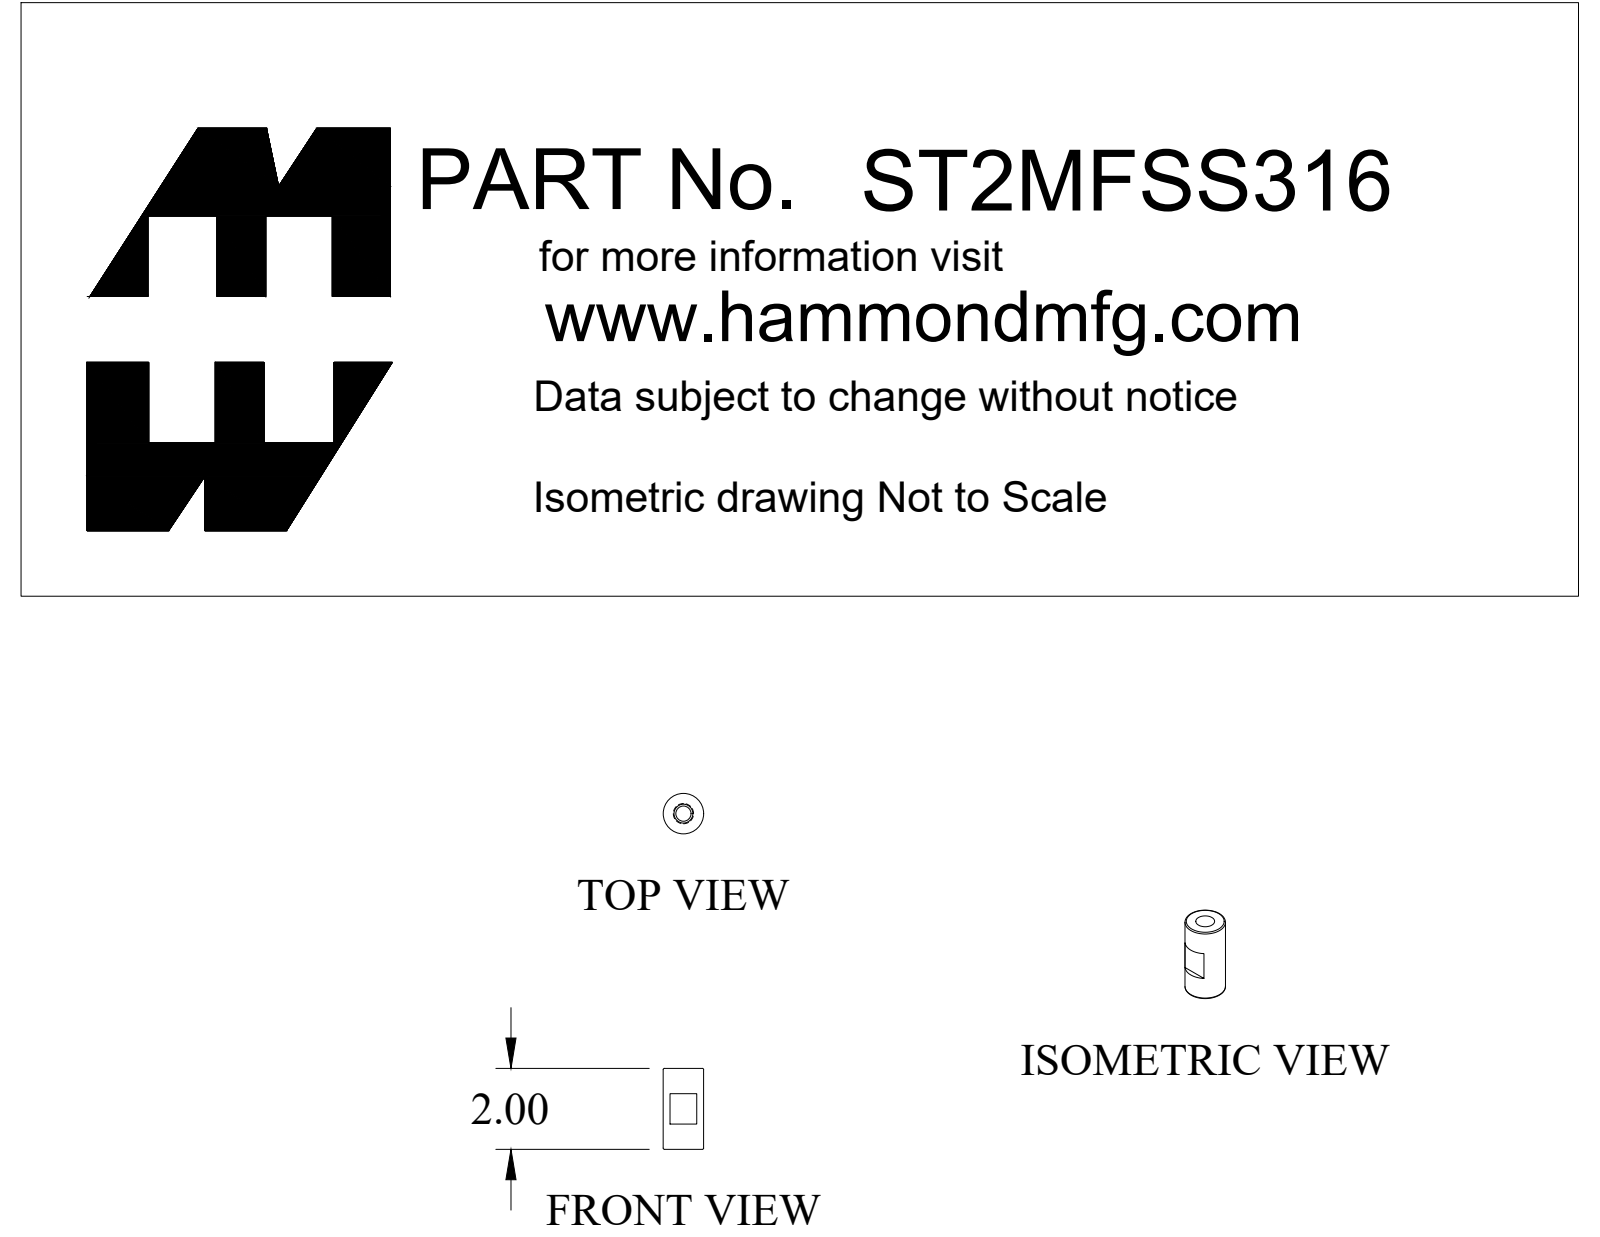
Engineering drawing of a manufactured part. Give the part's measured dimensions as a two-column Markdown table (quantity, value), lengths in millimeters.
| quantity | value |
| --- | --- |
| part name | ST2MFSS316 |
| STEP written by | SolidWorks 2019 (CONFIG_CONTROL_DESIGN) |
| units | millimeters |
| bodies | 3 solids, 31 faces (21 planar, 7 cylindrical, 3 other) |
| overall size | 61.4 × 25.4 × 25.4 |
| volume | 25 040 mm³ |
| surface area | 9 658 mm² |
| round holes (diameter × count) | 9.5 × 1, 11.8 × 1, 13.5 × 1 |
| round bosses / shafts (diameter × count) | 25.4 × 1, 12.7 × 1 |
| main face-to-face distances | 2.7, 19.1, 50.8, 53.5, 61.4, 10.6, 8, 19.1, 15.9, 34.9 |
